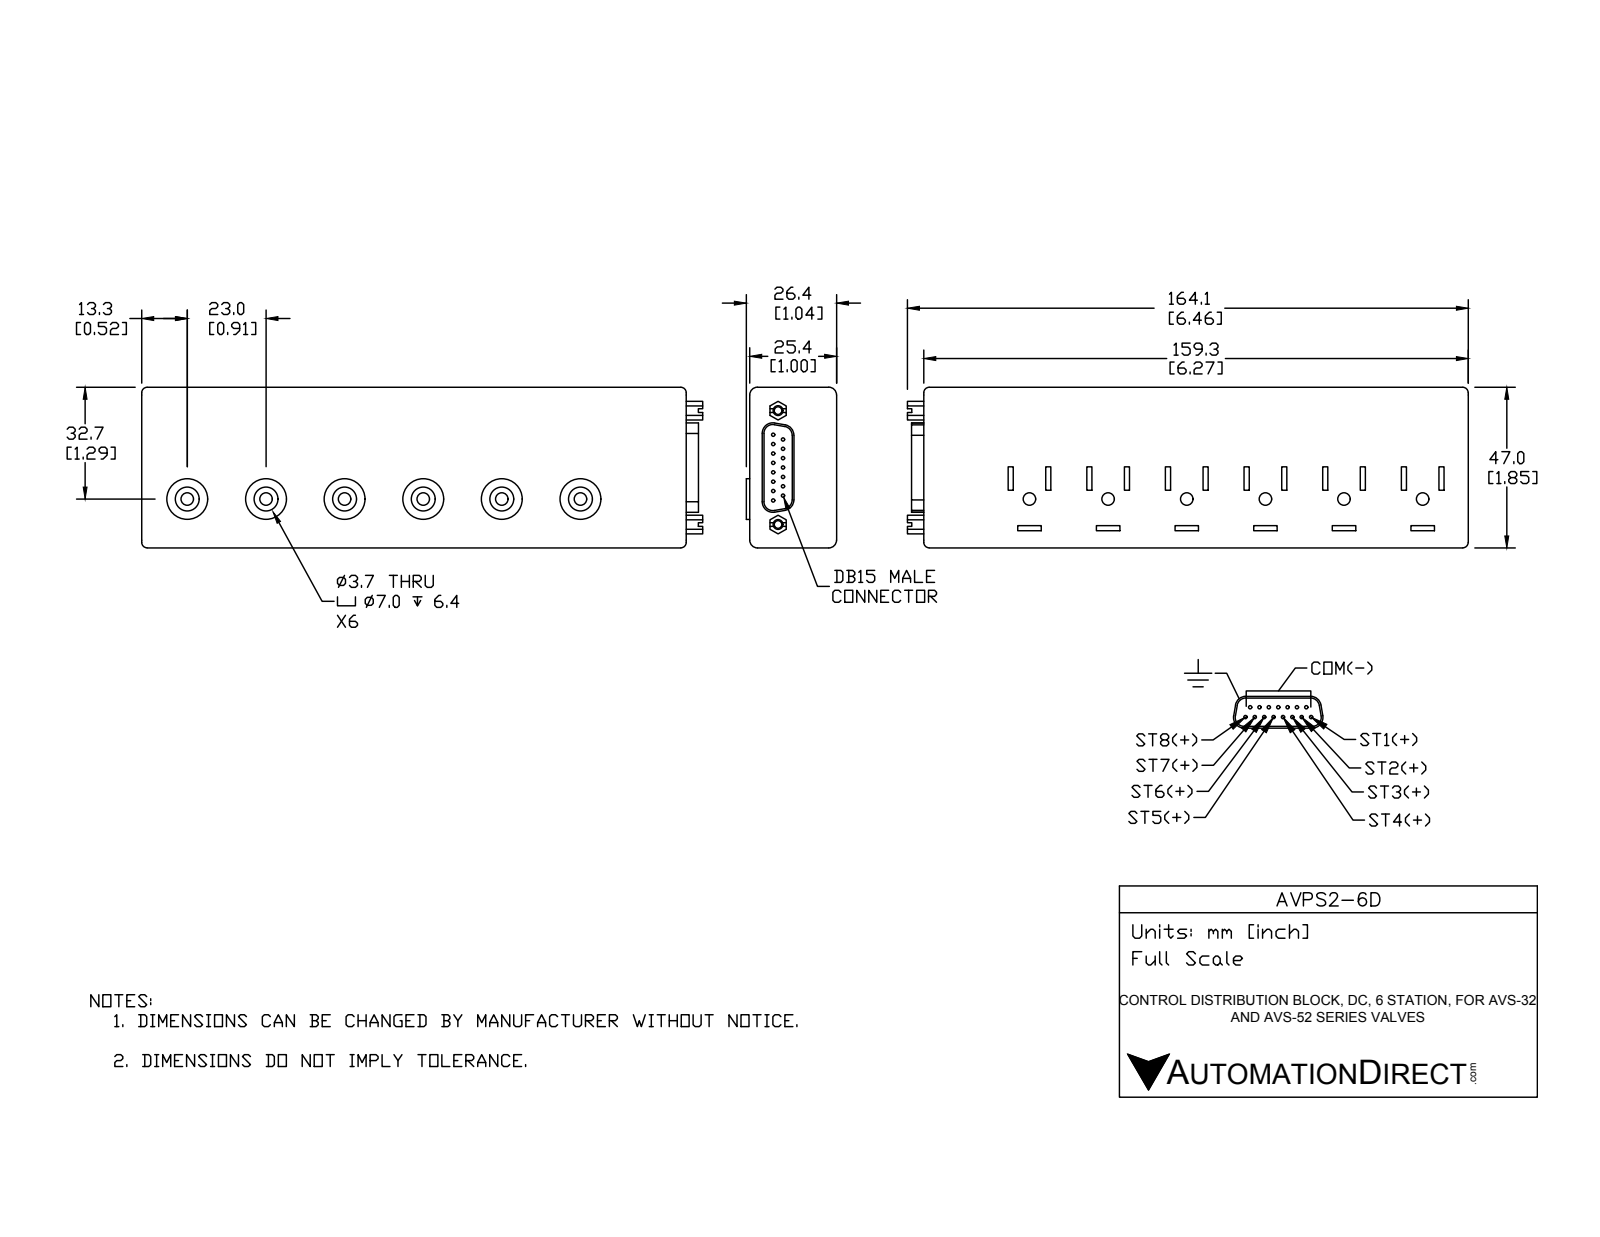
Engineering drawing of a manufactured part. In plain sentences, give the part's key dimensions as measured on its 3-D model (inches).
The part is named "AVPS2-6D". Its 3-D file was written by "SolidWorks 2016 (AUTOMOTIVE_DESIGN)". It is 1 solid with 265 faces: 161 planar, 92 cylindrical and 12 other. Overall it measures 6.461 by 1.85 by 1.04 inches. Its volume is 11.34 cubic inches and its surface area 46.49 square inches. Round holes: 6 of diameter 0.145, 6 of diameter 0.275, 2 of diameter 0.089. Round bosses or shafts: 15 of diameter 0.039, 6 of diameter 0.469. Partial cylindrical surfaces (rounded edges, fillets, slot ends): 8 of radius 0.062, 4 of radius 0.09, 4 of radius 0.102, 4 of radius 0.122. The main face-to-face distances are 1, 1.85, 6.272, 0.059, 0.04, 1.04, 0.906, 0.25, 0.79, 1.812. The hole center spacings are 0.906, 1.812, 1.812, 2.718, 3.624, 0.906, 1.311, 2.718.
